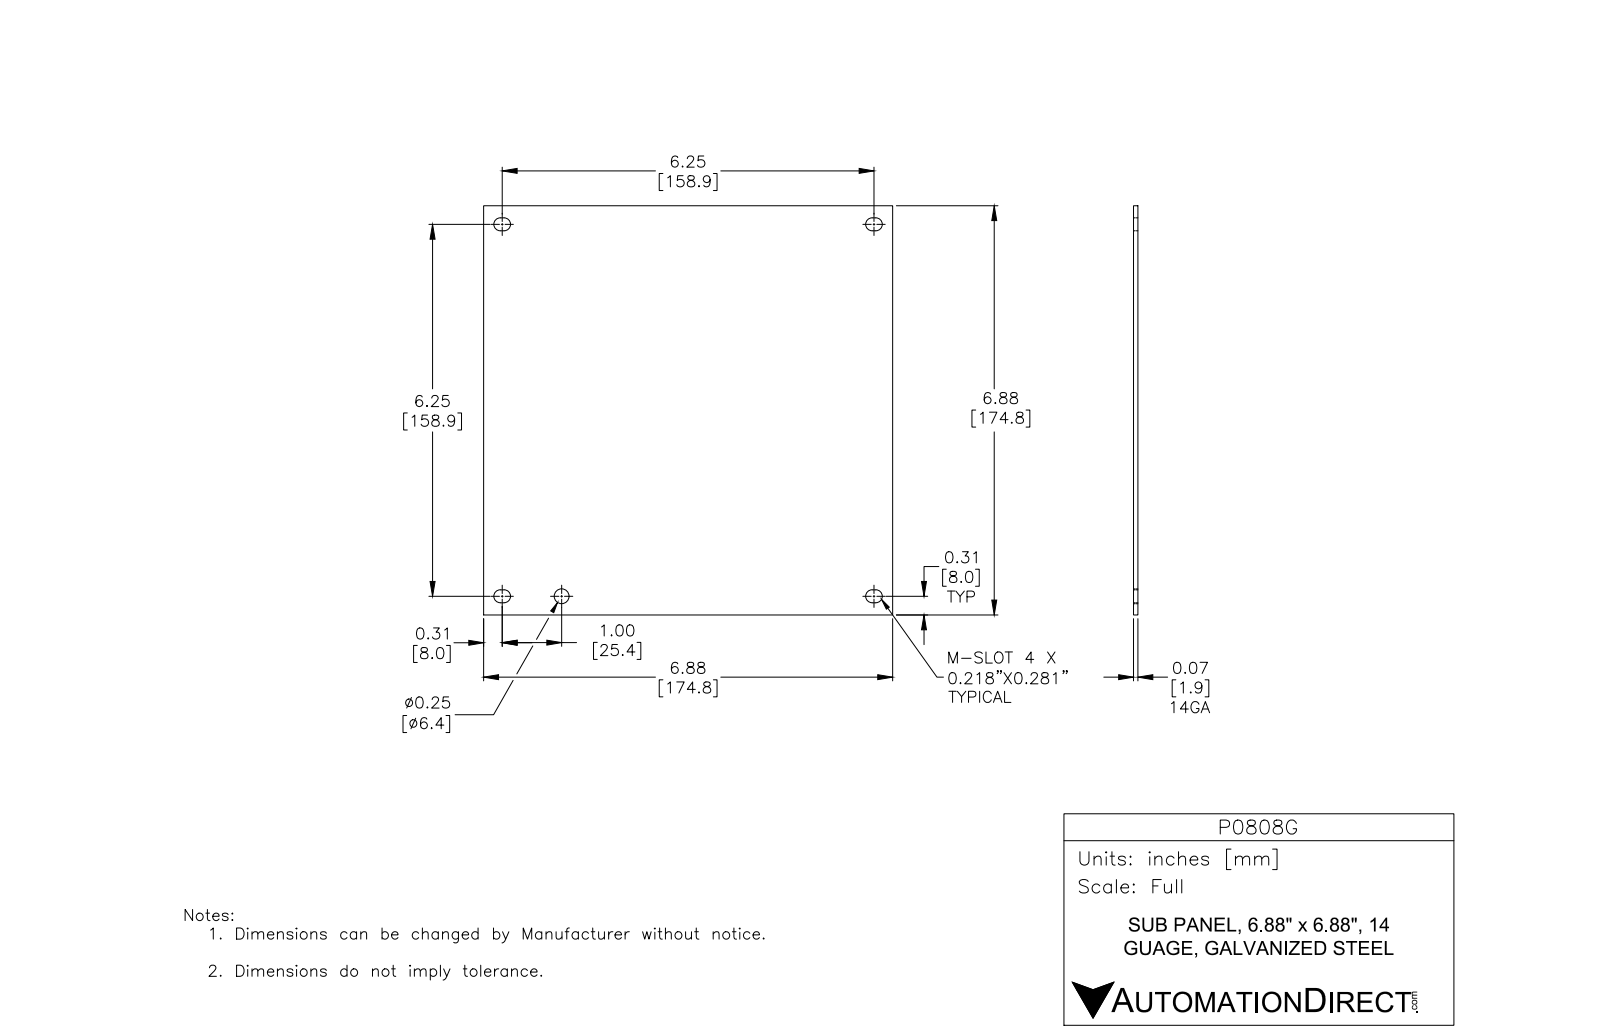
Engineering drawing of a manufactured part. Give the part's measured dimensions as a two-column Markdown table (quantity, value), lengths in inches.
| quantity | value |
| --- | --- |
| part name | P0808G |
| STEP written by | Autodesk Inventor 2012 (AUTOMOTIVE_DESIGN) |
| units | inches |
| bodies | 1 solid, 23 faces (14 planar, 9 cylindrical, 0 other) |
| overall size | 6.88 × 6.88 × 0.074 |
| volume | 3.484 in³ |
| surface area | 96.5 in² |
| round holes (diameter × count) | 0.25 × 1 |
| partial cylindrical surfaces (radius × count) | 0.109 × 8 |
| main face-to-face distances | 0.074, 6.88, 0.204, 0.422, 6.458, 6.676, 0.218, 6.254, 6.472, 6.036 |
